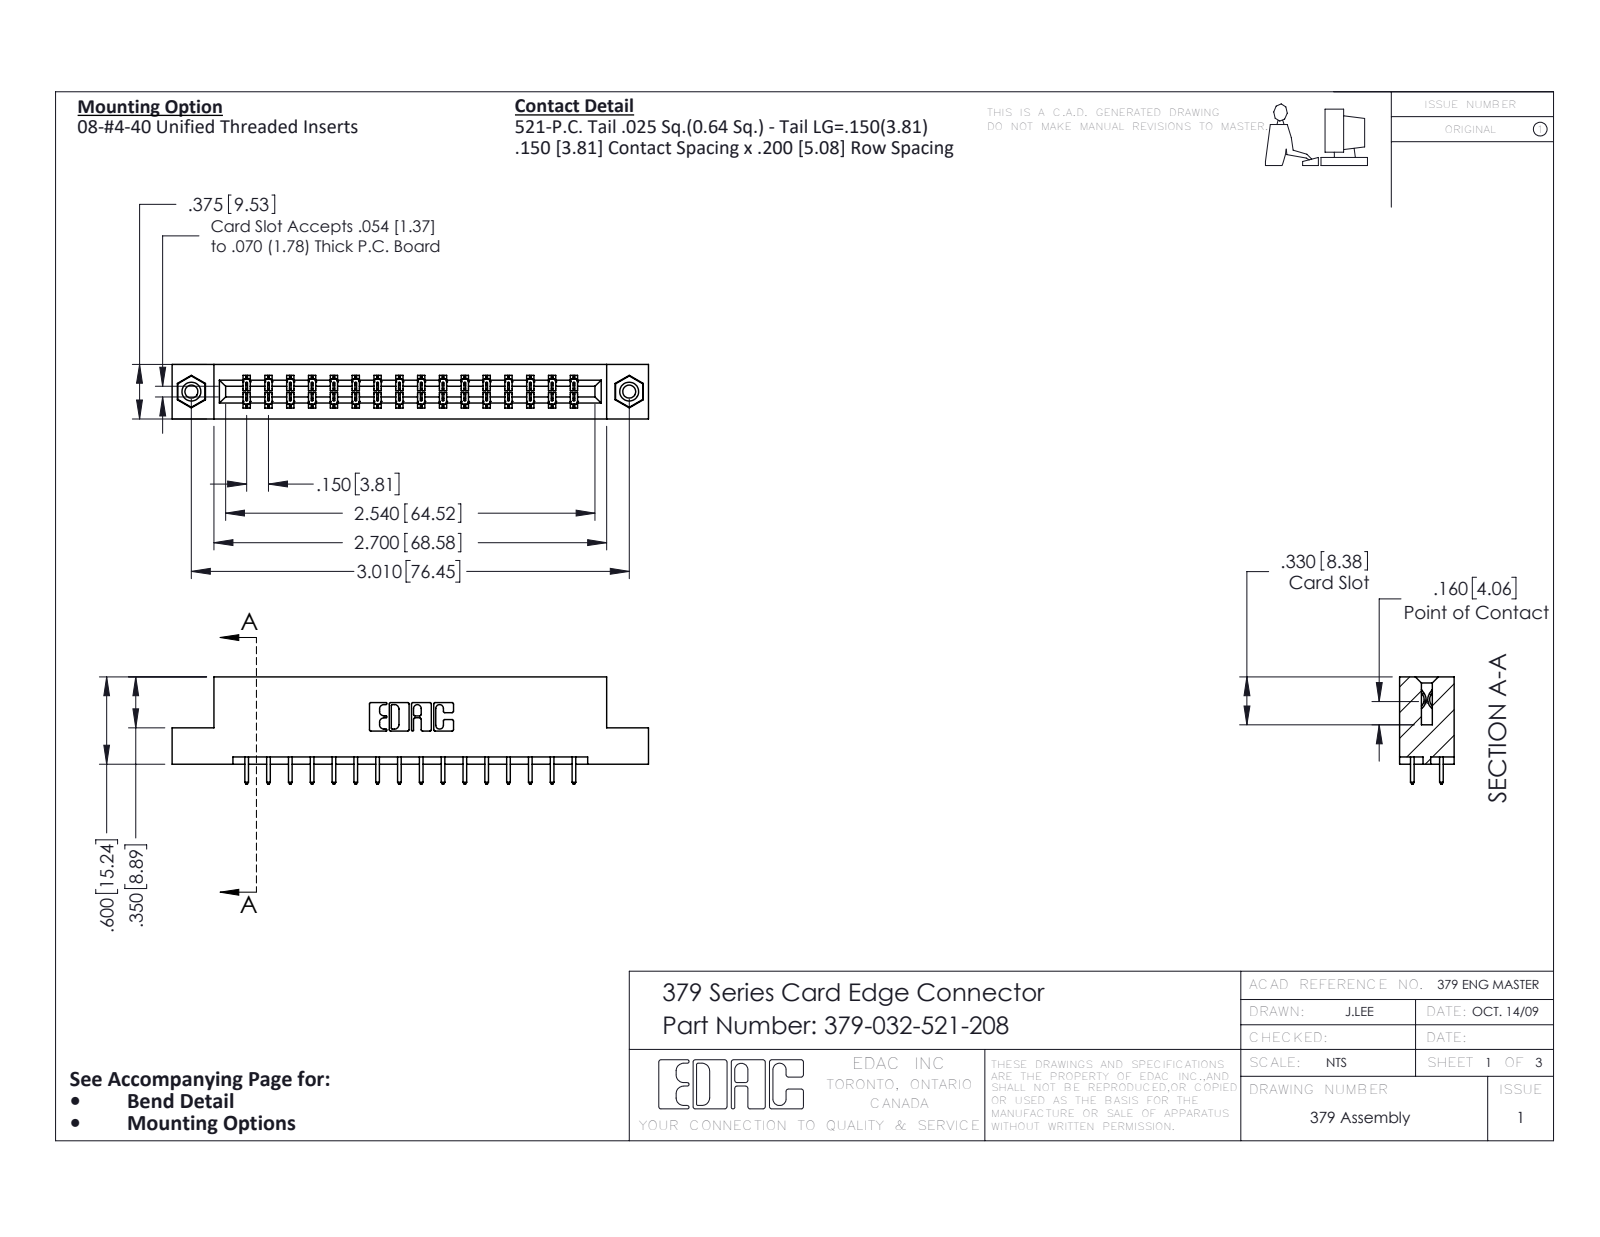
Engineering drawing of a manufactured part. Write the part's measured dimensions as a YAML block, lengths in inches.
part_name: "345-292-001_345-293-121; 345-250-001_345-250-003-102; 379 Part_Flush - .156 Dia - TI; 379-032-521-208"
step_written_by: "SolidWorks 2020 (CONFIG_CONTROL_DESIGN)"
units: inches
bodies: {solids: 35, faces: 1838, planar: 1254, cylindrical: 568, other: 16}
overall_size: [3.275, 0.737, 0.375]
volume: 0.52
surface_area: 14.34
round_holes:
  - {diameter: 0.089, count: 2}
  - {diameter: 0.125, count: 2}
  - {diameter: 0.156, count: 2}
round_bosses_or_shafts:
  - {diameter: 0.155, count: 2}
partial_cylinders:
  - {radius: 0.006, count: 63}
  - {radius: 0.01, count: 32}
  - {radius: 0.01, count: 22}
  - {radius: 0.007, count: 6}
  - {radius: 0.031, count: 6}
  - {radius: 0.026, count: 3}
  - {radius: 0.014, count: 2}
  - {radius: 0.022, count: 2}
face_to_face_distances: [0.3, 0.075, 0.375, 0.2, 0.1, 0.15, 0.05, 0.6, 0.225, 0.55]
hole_center_spacings: [3.01]
